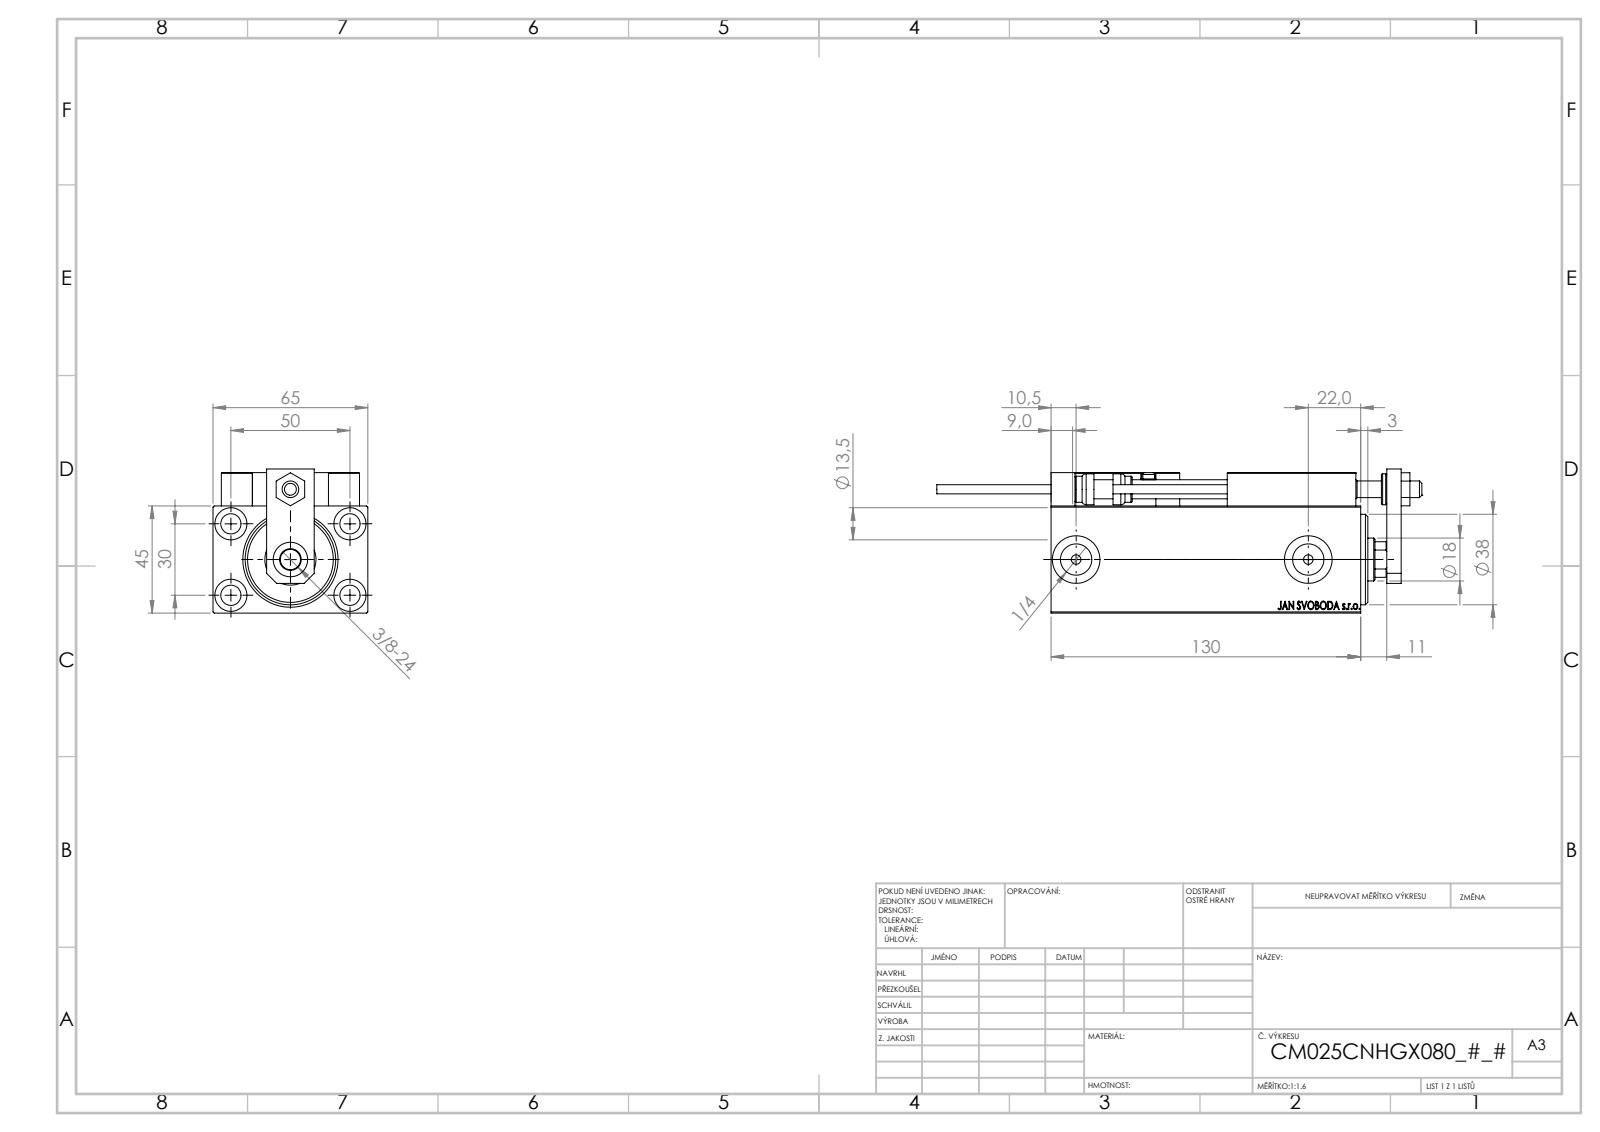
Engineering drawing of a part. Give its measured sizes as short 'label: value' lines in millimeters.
name: V450CM_C_Body; V450CM_C_VCP; V450CM_VC_B; NUT_D12 (+8 more)
written by: SolidWorks 2019 (CONFIG_CONTROL_DESIGN)
unit: mm
bodies: 23 solids, 1282 faces (560 planar, 188 cylindrical, 534 other)
size: 203.7 × 65 × 60.5
volume: 373 805 mm³; area: 99 913 mm²
holes: 6× ⌀4, 5× ⌀8, 5× ⌀8.5, 4× ⌀3.2, 4× ⌀13.5, 2× ⌀5, 2× ⌀13.16, 2× ⌀20, 1× ⌀7, 1× ⌀14.5, 1× ⌀18, 1× ⌀21.5
bosses: 2× ⌀5, 2× ⌀3.8, 1× ⌀13, 1× ⌀11
rounds: 30× R0.3, 2× R3, 1× R8.5
face distances: 45, 65, 14, 6, 59, 3, 13, 3.5, 7, 20
hole spacings: 29.15, 11.37, 20, 28.9, 29.59, 29.69, 30, 36.06
